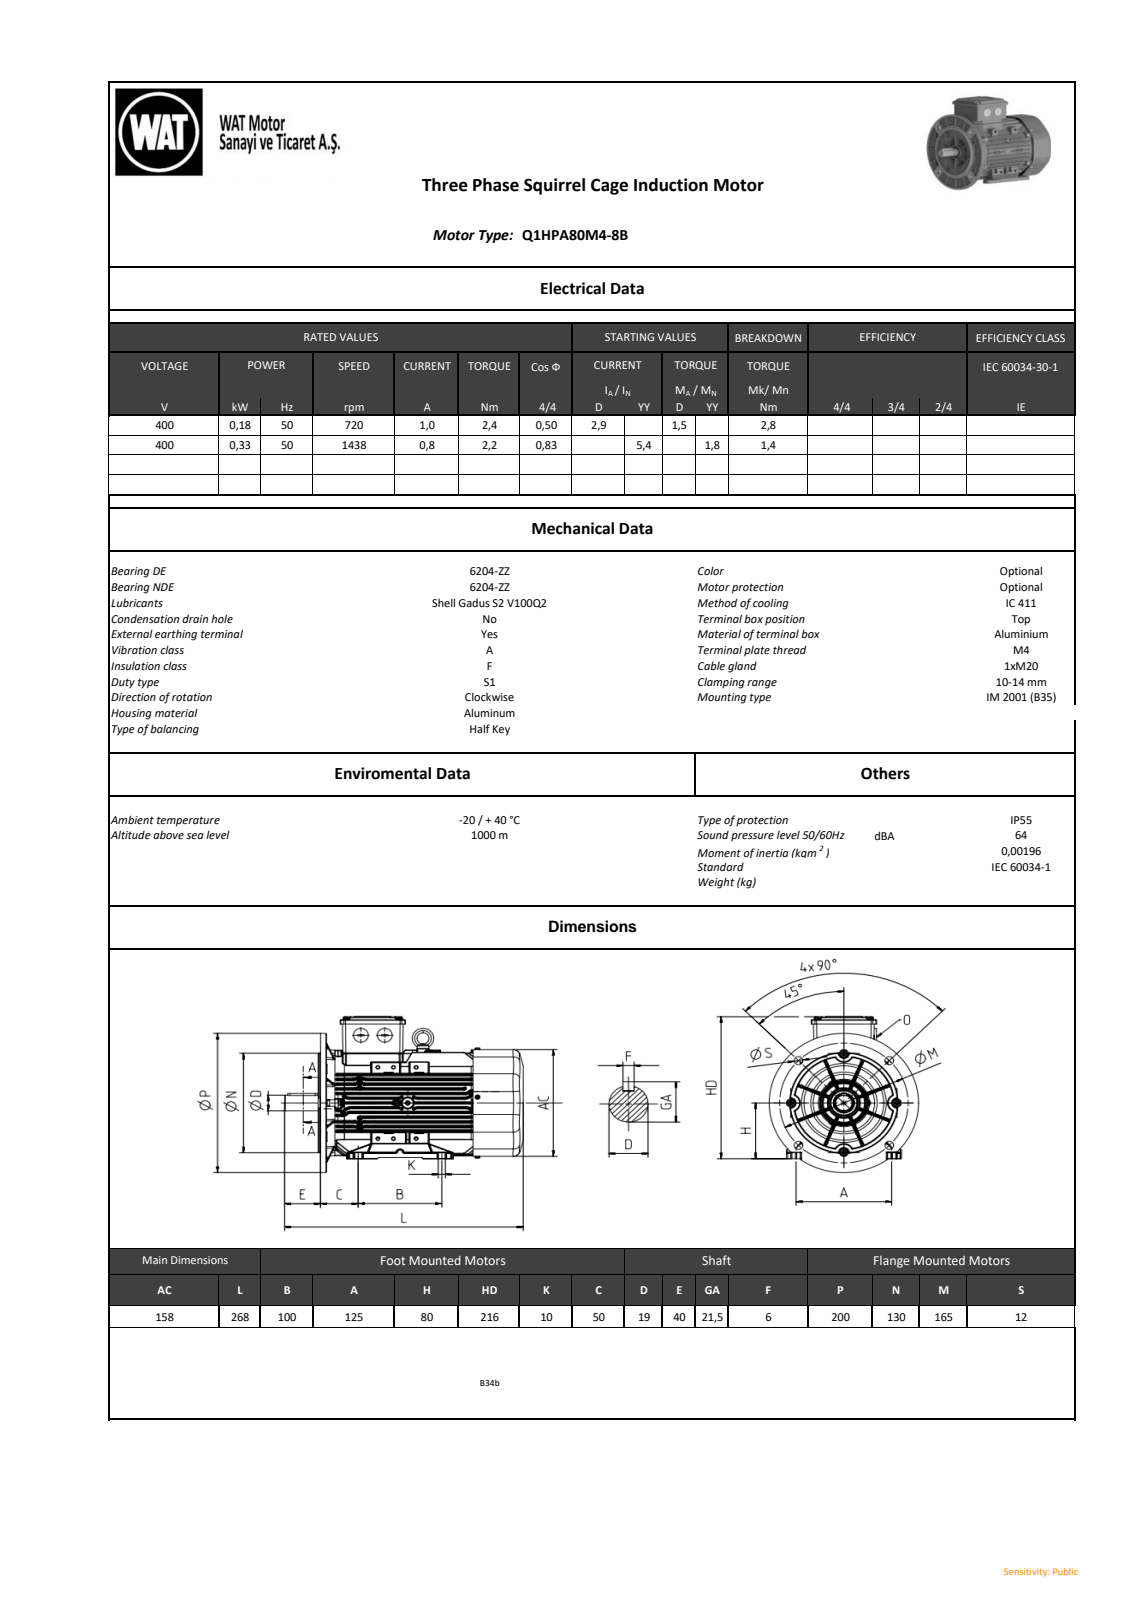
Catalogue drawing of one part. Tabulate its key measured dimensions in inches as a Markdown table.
| quantity | value |
| --- | --- |
| part name | model1 |
| STEP written by | SIEMENS PLM Software NX2206.8101 (AUTOMOTIVE_DESIGN) |
| units | inches |
| bodies | 0 solids, 6686 faces (1259 planar, 2617 cylindrical, 2810 other) |
| overall size | 10.551 × 9.272 × 7.874 |
| round holes (diameter × count) | 0.181 × 2, 0.197 × 1, 0.315 × 1, 2.244 × 1 |
| round bosses / shafts (diameter × count) | 0.236 × 8, 0.842 × 2, 5.768 × 1, 5.118 × 1, 2.402 × 1, 0.948 × 1, 0.795 × 1, 0.787 × 1 |
| partial cylindrical surfaces (radius × count) | 0.039 × 721, 0.02 × 573, 0.031 × 332, 0.079 × 128, 0.059 × 52, 0.197 × 26, 0.039 × 12, 0.059 × 10 |
| main face-to-face distances | 0.039, 6.181, 1.652, 0.161, 0.408, 6.18, 0.317, 0.156, 3.386, 0.709 |
| hole center spacings | 2.793 |
